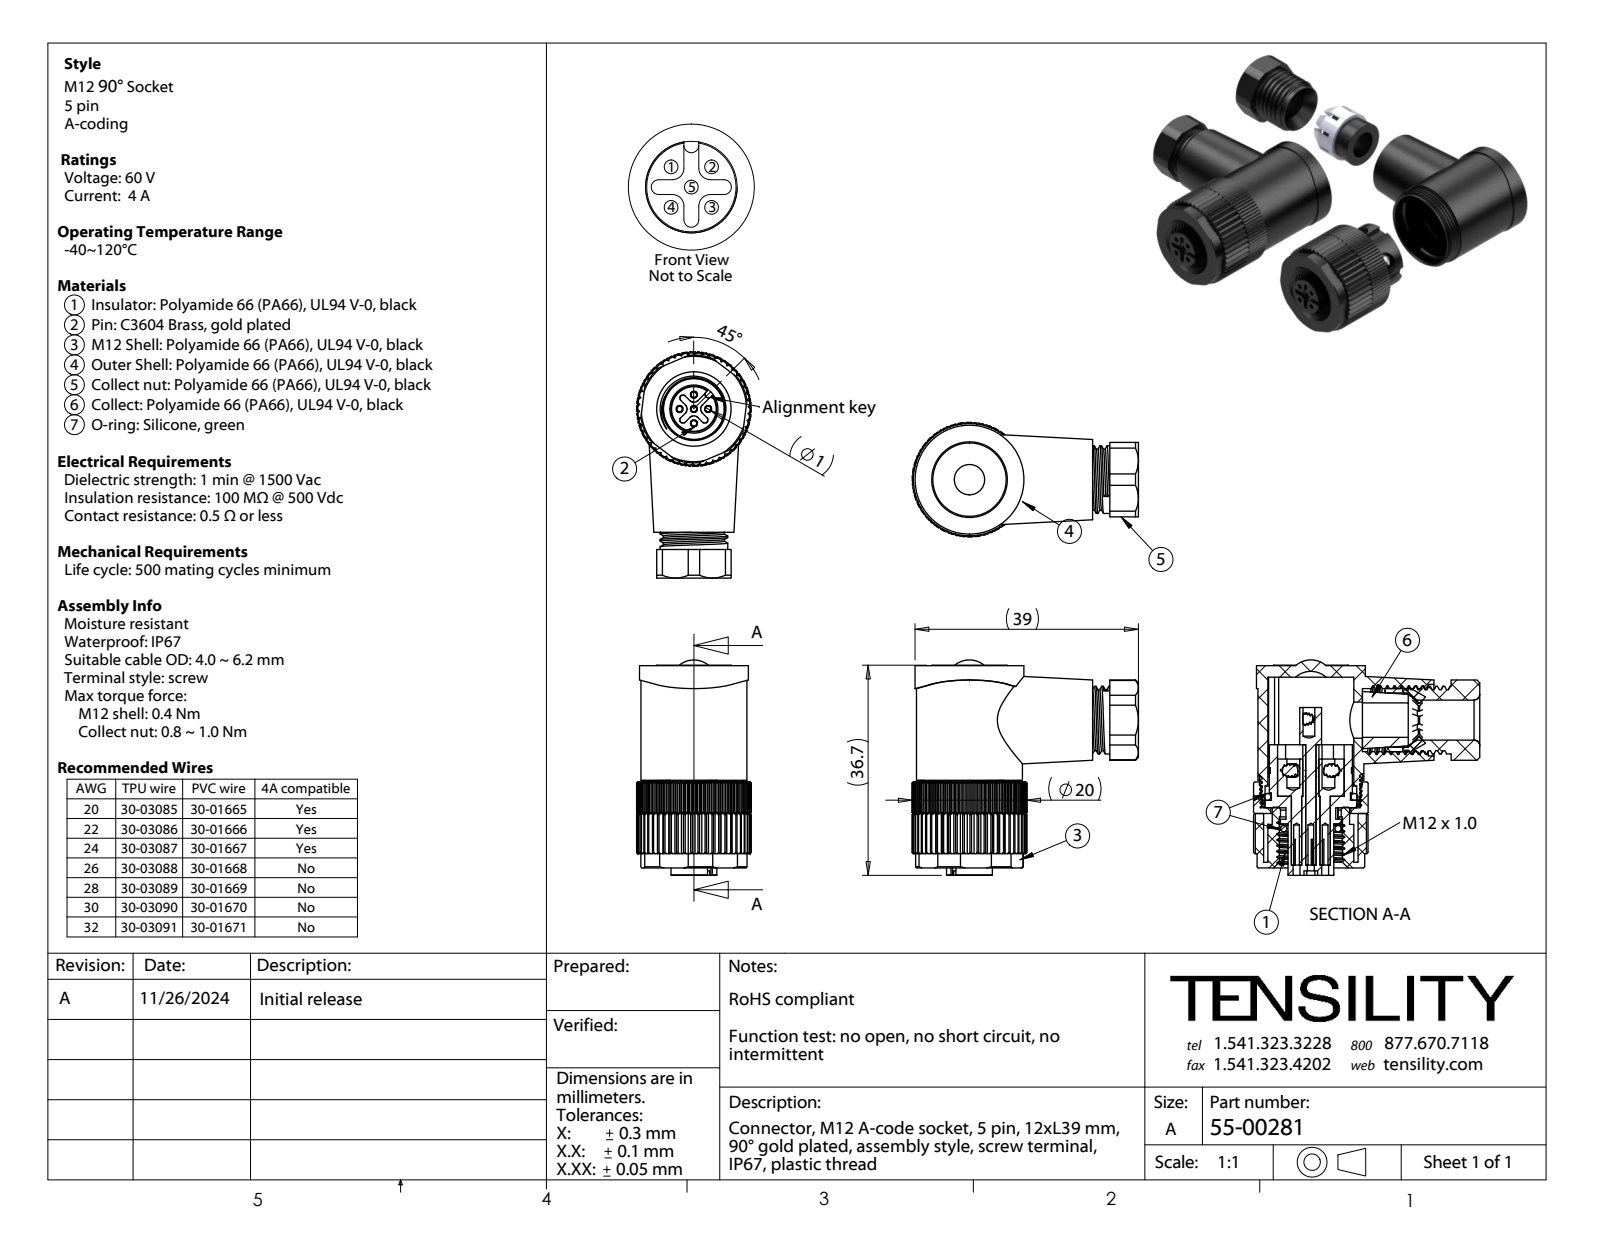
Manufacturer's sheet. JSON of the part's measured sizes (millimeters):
{"part_name": "55-00281-01; 55-00281-02; 55-00281-10; 55-00281-11 (+8 more)", "step_written_by": "SolidWorks 2021 (CONFIG_CONTROL_DESIGN)", "units": "millimeters", "bodies": {"solids": 18, "faces": 1520, "planar": 543, "cylindrical": 518, "other": 459}, "overall_size": [39.5, 37.6, 20], "volume_mm3": 8882, "surface_area_mm2": 14261, "round_holes": [[2.5, 9], [1, 5], [1.2, 5], [2.05, 5], [1.8, 4], [5, 4], [11, 2], [6, 1], [6.3, 1], [7, 1], [9.5, 1], [10.6, 1]], "round_bosses_or_shafts": [[3.5, 5], [2.4, 5], [19, 1], [18.5, 1], [17.8, 1], [17.03, 1], [17, 1], [14.5, 1]], "partial_cylinders_radius": [[1.75, 5], [1, 4], [0.55, 3], [0.6, 1], [6.45, 1], [6.5, 1], [7, 1], [9.4, 1]], "face_to_face_distances": [1, 2, 22.8, 24.8, 25.8, 9.5, 11.8, 12.5, 13.44, 13.8], "hole_center_spacings": [5.14, 5.13, 0.8, 2.5, 3.12, 3.54, 3.62, 4.34]}
